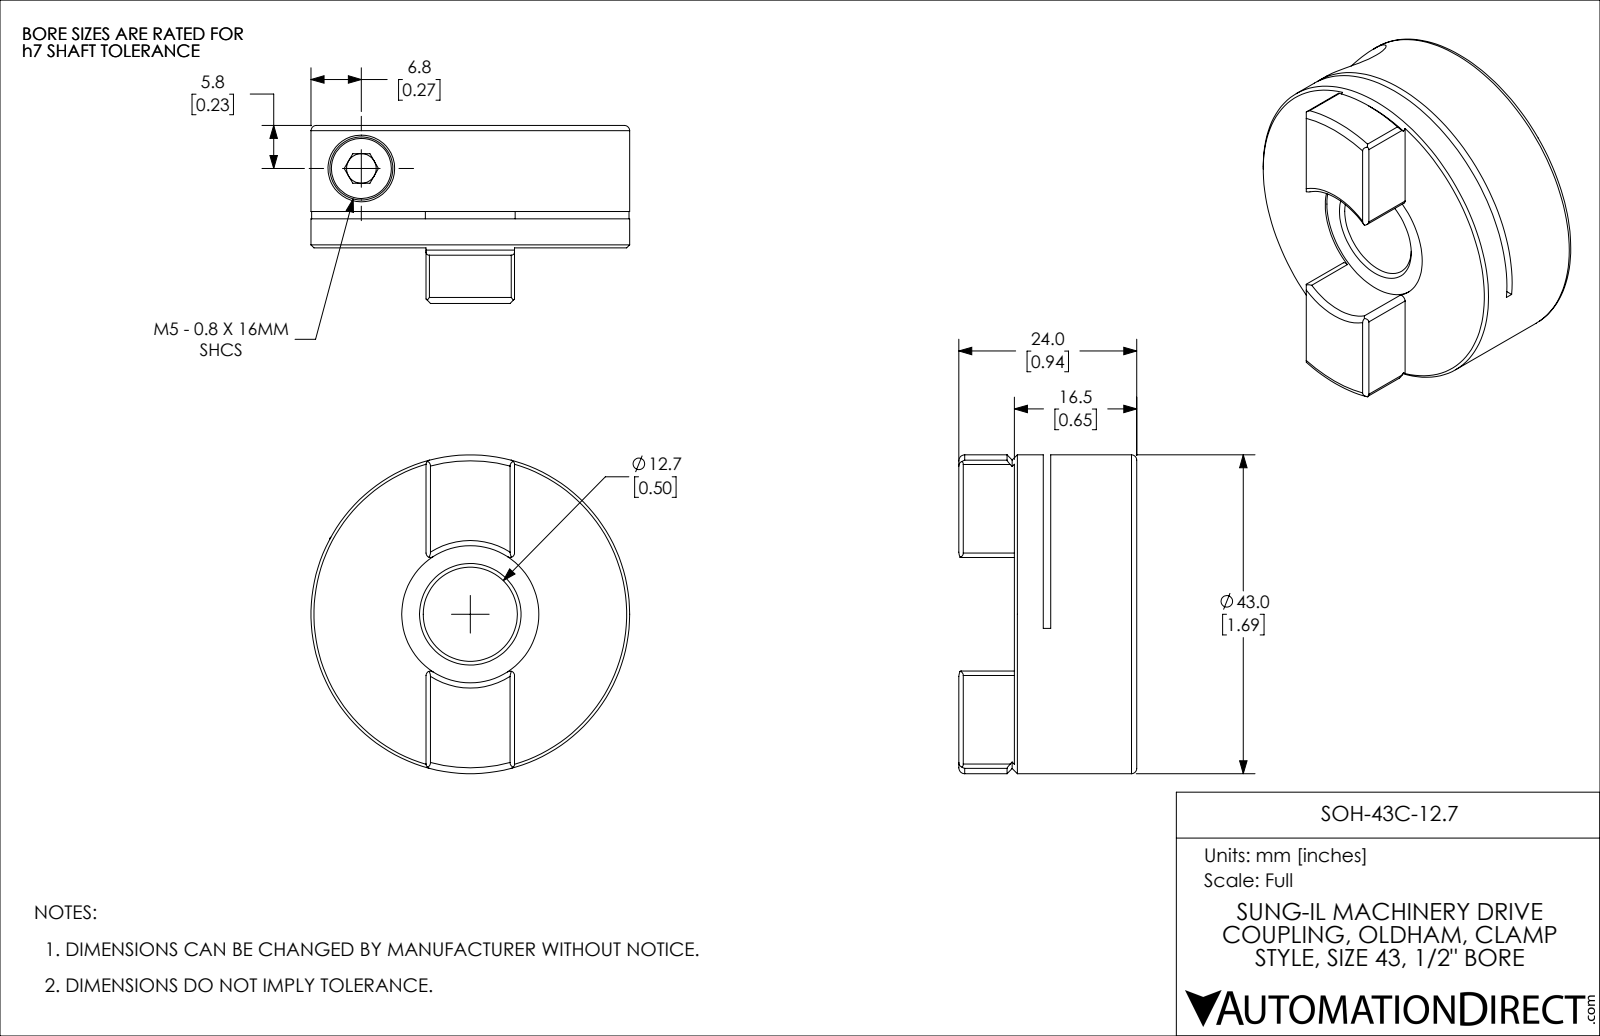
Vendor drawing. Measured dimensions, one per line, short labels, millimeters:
name: SOH-43C-12
written by: SolidWorks 2021 (CONFIG_CONTROL_DESIGN)
unit: mm
bodies: 2 solids, 95 faces (39 planar, 33 cylindrical, 23 other)
size: 43 × 43 × 24
volume: 22 808 mm³; area: 8 980 mm²
holes: 1× ⌀4, 1× ⌀4.2, 1× ⌀5.4, 1× ⌀9, 1× ⌀12, 1× ⌀18.5
bosses: 1× ⌀43, 1× ⌀8.5, 1× ⌀5
rounds: 8× R0.6, 1× R37.5
face distances: 16.5, 12.6, 3.9, 11.6, 1, 4.9, 12.4, 24, 11.4, 7.5
